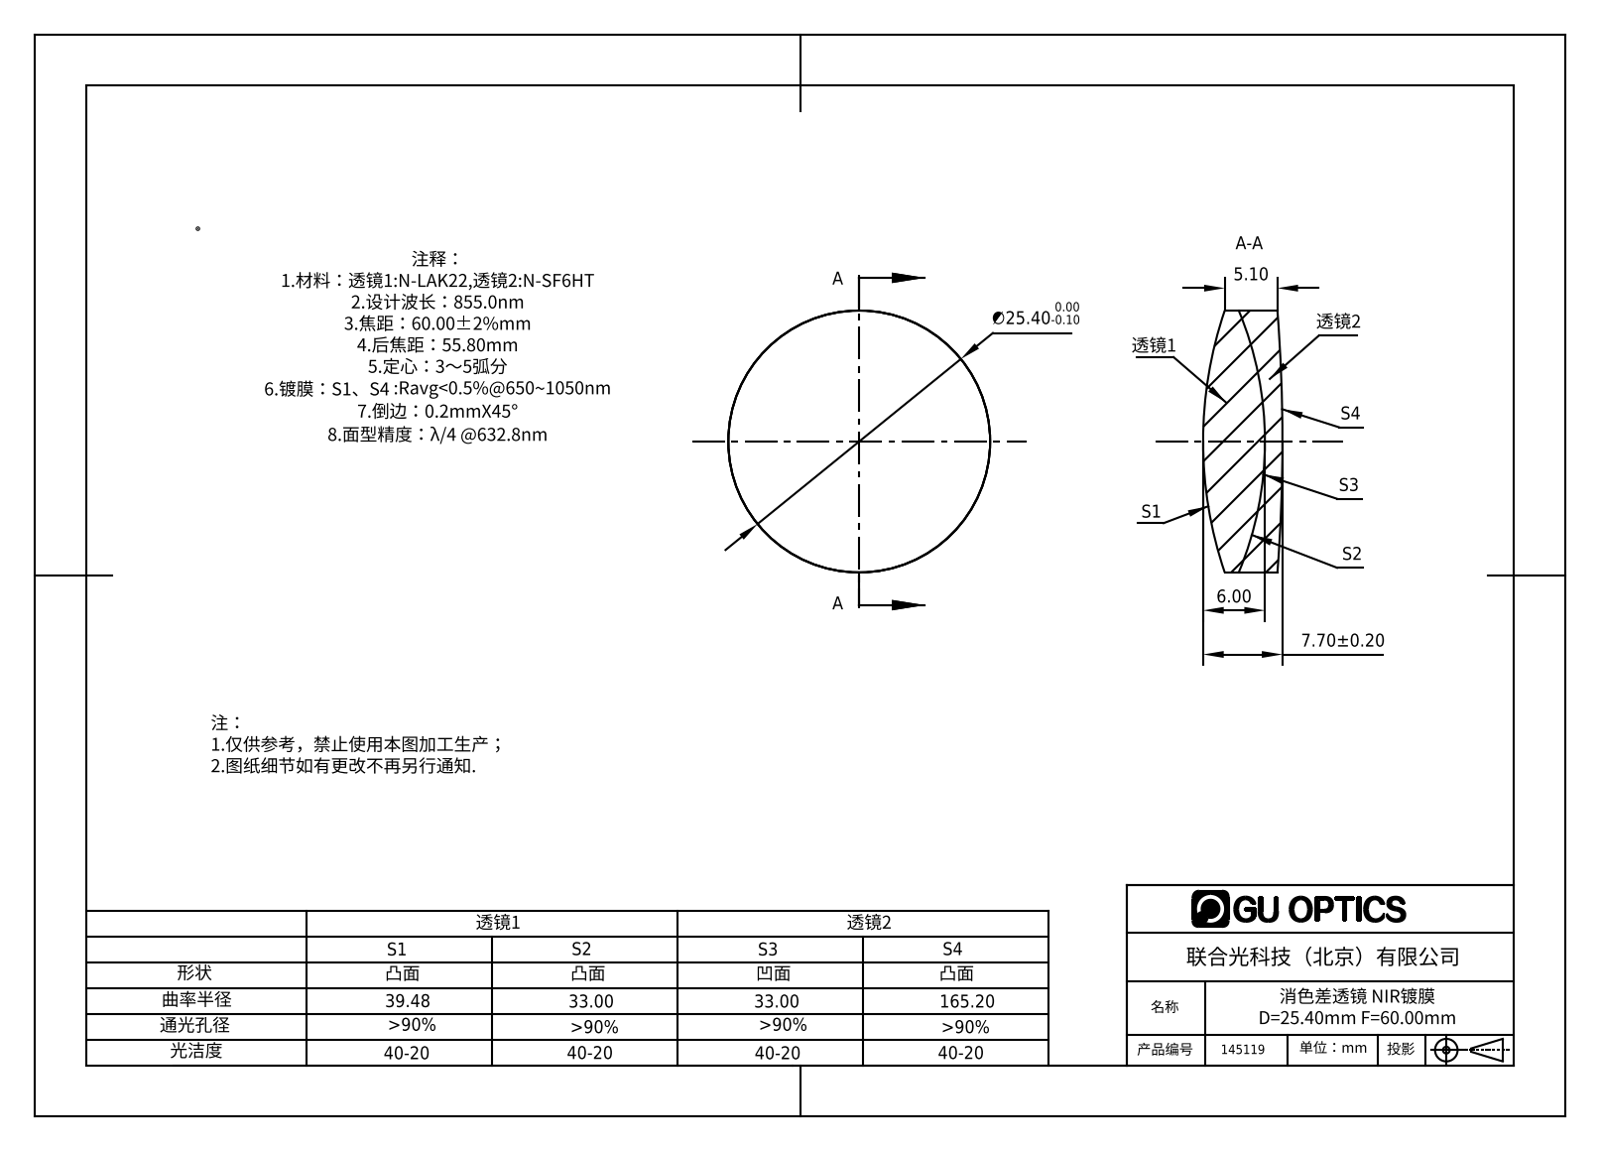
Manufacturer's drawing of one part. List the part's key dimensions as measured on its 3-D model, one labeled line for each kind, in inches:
Part name (STEP PRODUCT): 145119
STEP written by: SolidWorks 2016 (AUTOMOTIVE_DESIGN)
Units: inches
Bodies: 2 solids, 12 faces (0 planar, 4 cylindrical, 8 other)
Overall size (bounding box): 1 × 1 × 0.303
Volume: 0.198 in³ · Surface area: 3.86 in²
Round bosses / shafts (diameter × count): ⌀1 ×1
